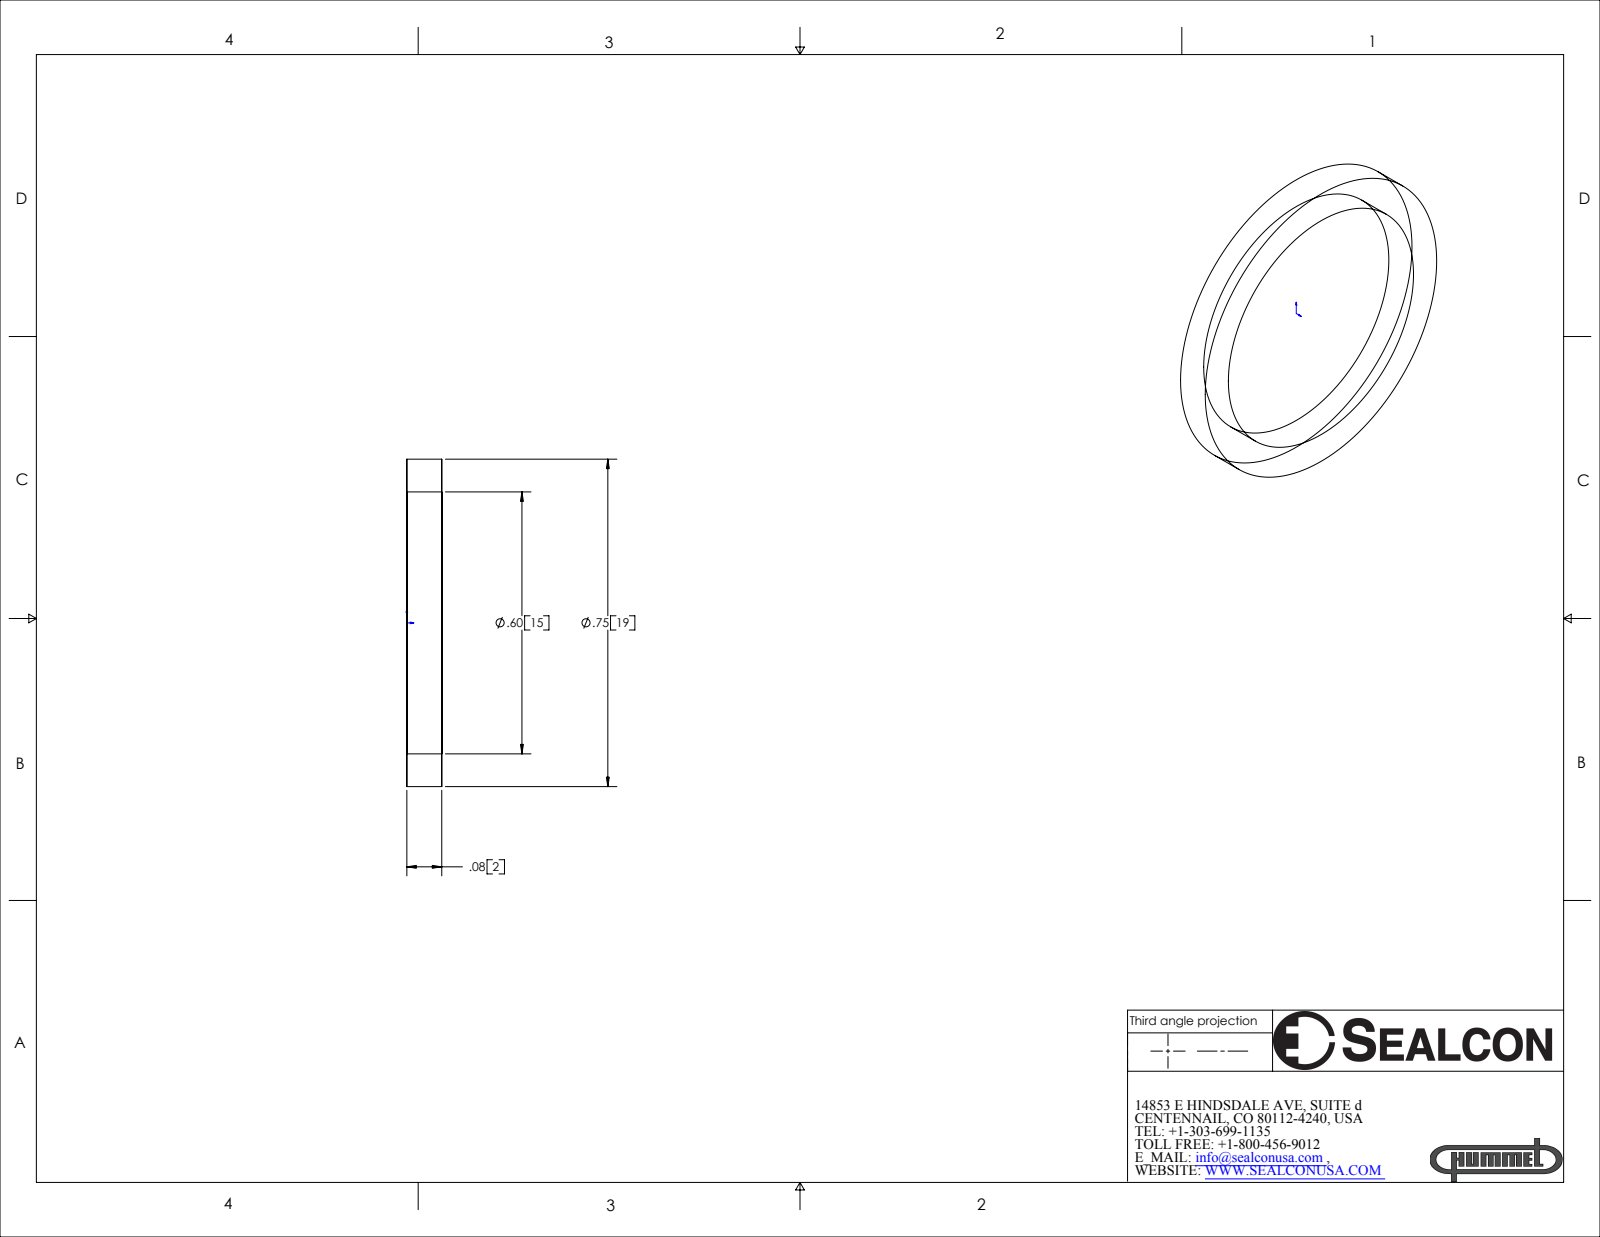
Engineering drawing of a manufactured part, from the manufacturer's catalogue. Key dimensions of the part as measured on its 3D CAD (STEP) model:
Part name (STEP PRODUCT): SR-09-NY
STEP written by: SolidWorks 2007 (CONFIG_CONTROL_DESIGN)
Units: inches
Bodies: 1 solid, 6 faces (2 planar, 4 cylindrical, 0 other)
Overall size (bounding box): 0.75 × 0.75 × 0.08
Volume: 0.013 in³ · Surface area: 0.657 in²
Round holes (diameter × count): ⌀0.6 ×1
Round bosses / shafts (diameter × count): ⌀0.75 ×1
Main face-to-face distances: 0.08
